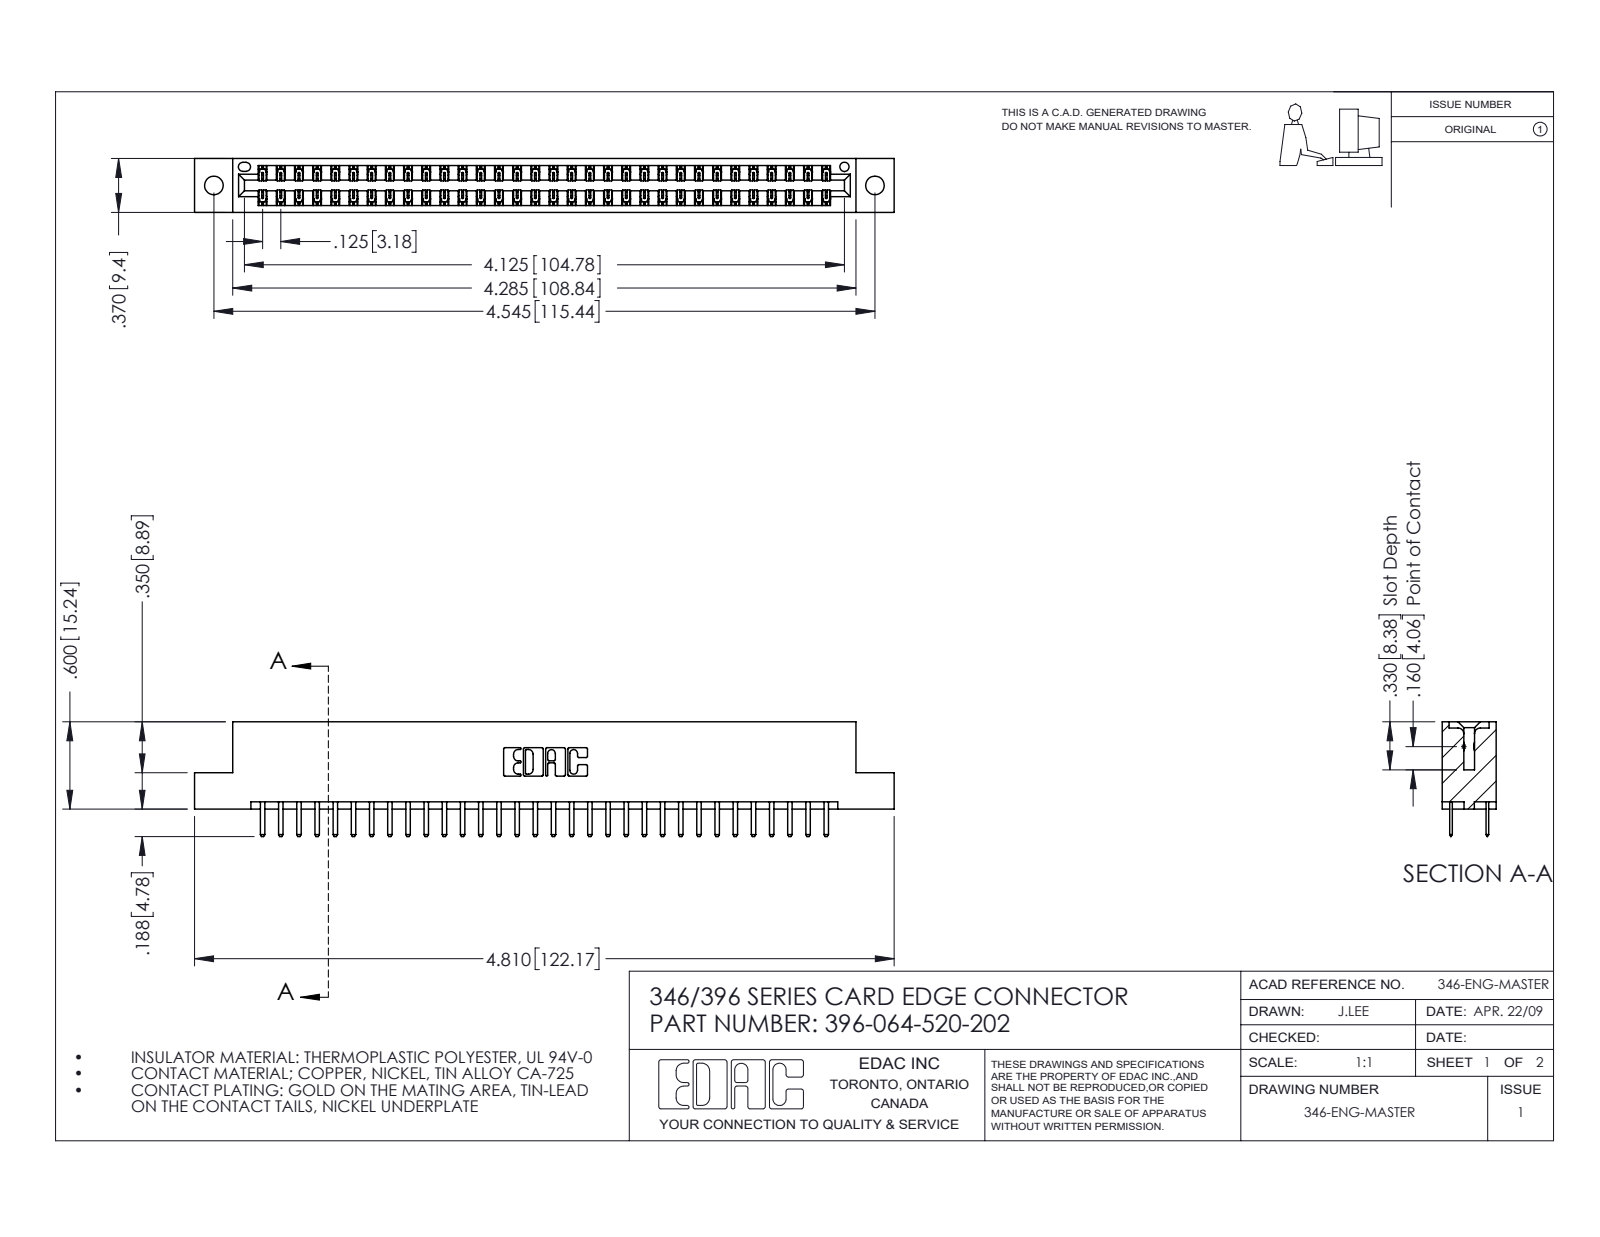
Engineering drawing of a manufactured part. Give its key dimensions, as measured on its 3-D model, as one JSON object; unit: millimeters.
{"part_name": "346 Part_Flush Mounting Lugs - 0.128 Dia; 396-064-520-202; 345-292-001_345-293-120", "step_written_by": "SolidWorks 2016 (CONFIG_CONTROL_DESIGN)", "units": "millimeters", "bodies": {"solids": 65, "faces": 3706, "planar": 2444, "cylindrical": 1262, "other": 0}, "overall_size": [122.2, 20, 9.4], "volume_mm3": 11800, "surface_area_mm2": 15690, "round_holes": [[3.3, 2], [1.6, 1]], "partial_cylinders_radius": [[0.2, 96], [0.3, 68], [0.3, 22], [0.2, 6], [0.8, 6], [0.7, 3], [0.4, 2], [0.6, 2]], "face_to_face_distances": [1.2, 8.2, 6.4, 9.4, 7, 1.8, 7.6, 0.6, 3.8, 5.6], "hole_center_spacings": [6.2, 110.2, 115.4]}
